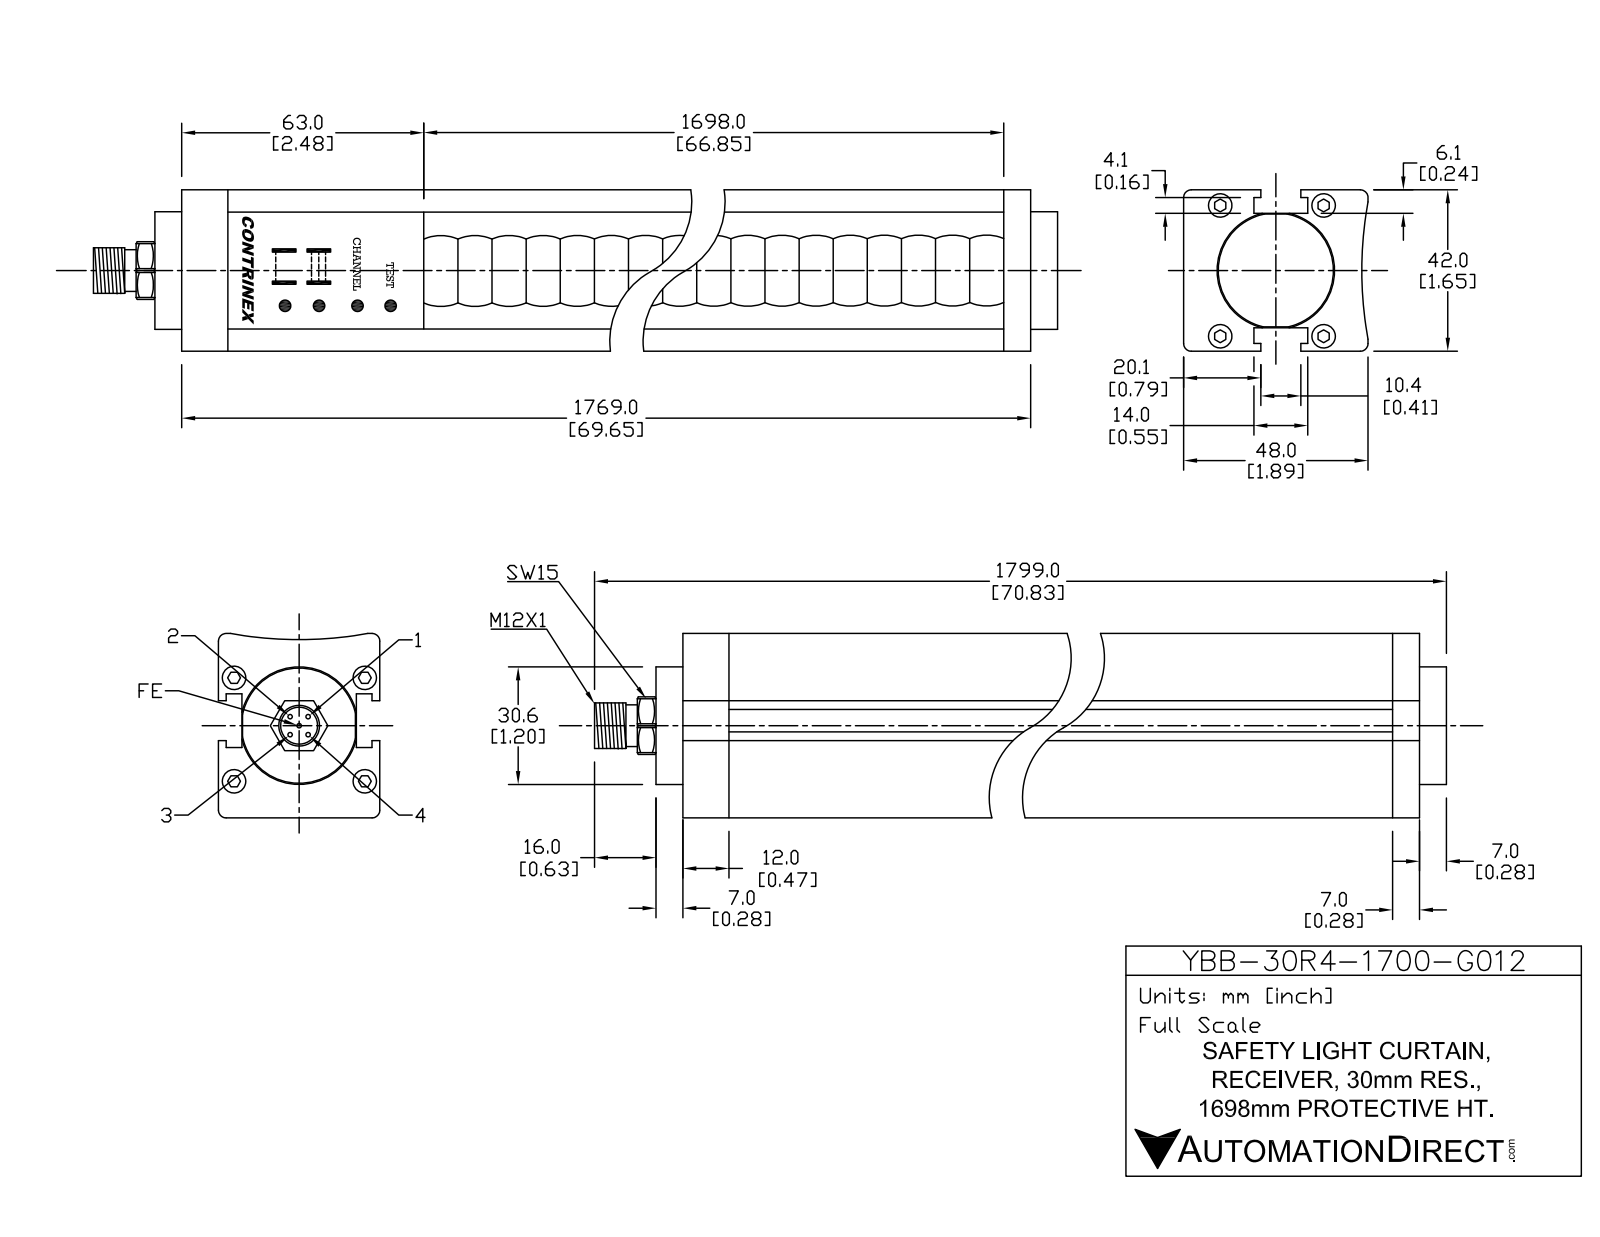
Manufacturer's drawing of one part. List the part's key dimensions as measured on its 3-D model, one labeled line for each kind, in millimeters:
Part name (STEP PRODUCT): YBB-30R4-1700-G012
STEP written by: SolidWorks 2016 (AUTOMOTIVE_DESIGN)
Units: millimetres
Bodies: 19 solids, 440 faces (208 planar, 168 cylindrical, 64 other)
Overall size (bounding box): 1799 × 48 × 42
Volume: 3 177 000 mm³ · Surface area: 394 749 mm²
Round holes (diameter × count): ⌀6 ×4, ⌀8.5 ×1, ⌀32 ×1
Round bosses / shafts (diameter × count): ⌀1 ×5, ⌀5.5 ×4, ⌀30.6 ×1, ⌀12 ×1, ⌀10.5 ×1
Partial cylindrical surfaces — rounded edges, fillets, slot ends (radius × count): R1 ×48, R0.5 ×4, R0.55 ×2, R8.2 ×1, R100 ×1
Main face-to-face distances: 6.3, 35.7, 42, 29.4, 14, 17.2, 31.2, 15.7, 29.7, 46.9
Hole centre spacings: 21.04, 22.34, 26.9, 34, 43.35
